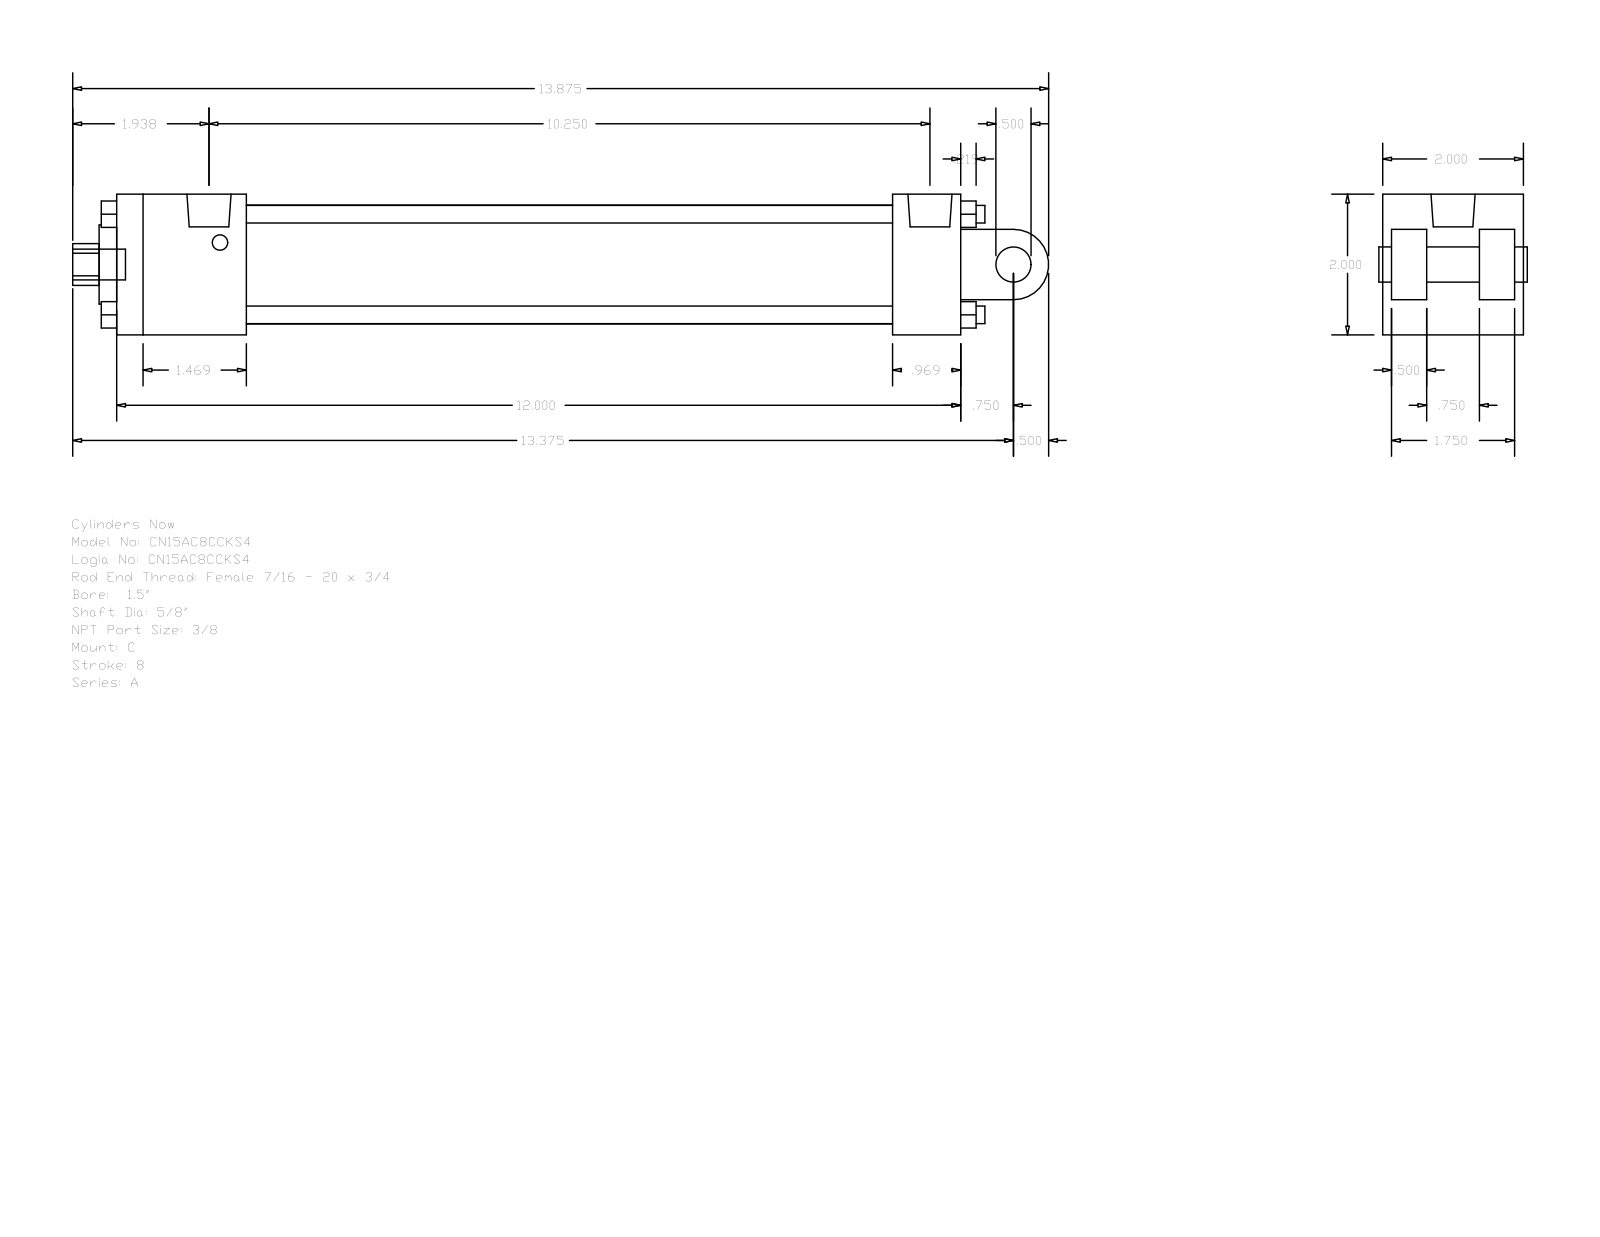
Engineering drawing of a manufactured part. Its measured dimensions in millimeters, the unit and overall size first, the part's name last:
Units: millimetres
Overall size (bounding box): 352.43 × 50.8 × 50.8
Round holes (diameter × count): ⌀5.56 ×2, ⌀15.88 ×1, ⌀15.93 ×1, ⌀28.57 ×1, ⌀42.93 ×1
Round bosses / shafts (diameter × count): ⌀6.35 ×4, ⌀5.56 ×2, ⌀15.93 ×1, ⌀12.7 ×1, ⌀11.11 ×1
Partial cylindrical surfaces — rounded edges, fillets, slot ends (radius × count): R7.54 ×1, R12.7 ×1
Main face-to-face distances: 50.8, 12.7, 304.8, 3.17, 15.87, 34.93, 47.63, 31.76, 280.19, 24.61
Hole centre spacings: 3.97
Bodies: 0 solids, 135 faces (102 planar, 33 cylindrical, 0 other)
Part name (STEP PRODUCT): A_C__0150_0.625
STEP written by: GSSL Pune (CONFIG_CONTROL_DESIGN)
